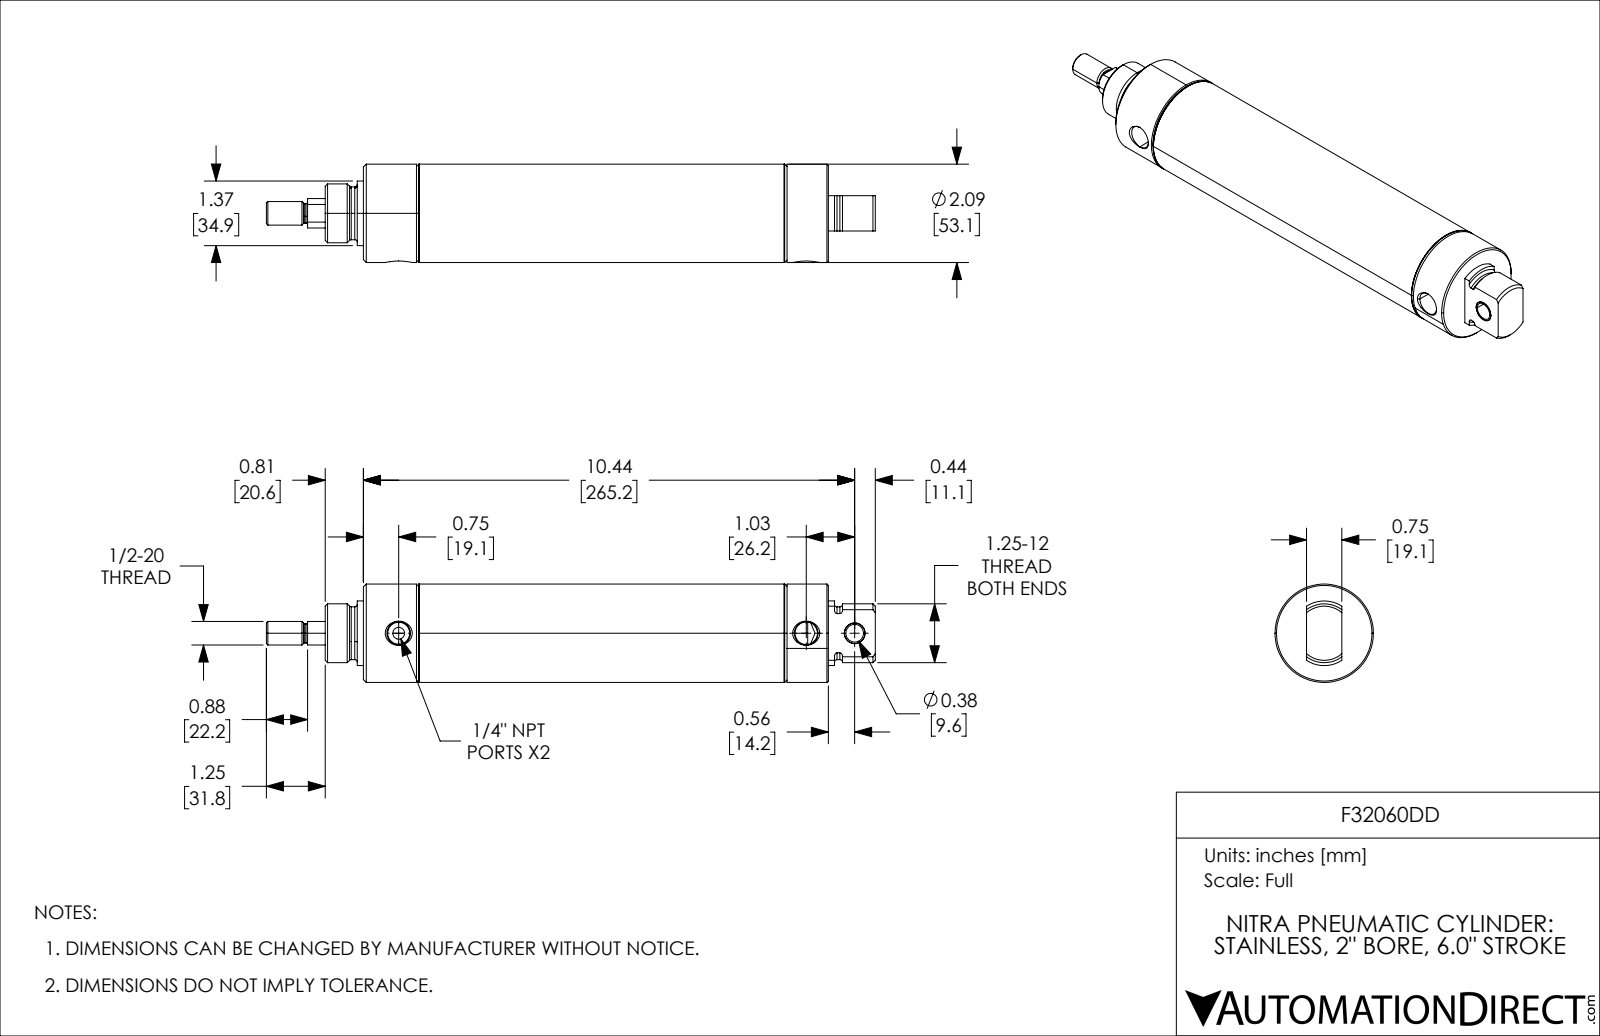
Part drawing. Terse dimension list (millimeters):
name: F32060DD_5; F32060DD_11; F32060DD_7; F32060DD (+2 more)
written by: SolidWorks 2021 (CONFIG_CONTROL_DESIGN)
unit: mm
bodies: 5 solids, 160 faces (31 planar, 60 cylindrical, 69 other)
size: 328.62 × 53.09 × 53.09
volume: 290 012 mm³; area: 119 561 mm²
holes: 1× ⌀6.35, 1× ⌀9.55, 1× ⌀11.15, 1× ⌀12.18, 1× ⌀16.52, 1× ⌀19.05, 1× ⌀49.05
bosses: 1× ⌀53.09, 1× ⌀51.16, 1× ⌀34.87, 1× ⌀31.75, 1× ⌀28.51, 1× ⌀15.88, 1× ⌀12.7, 1× ⌀10.46
rounds: 1× R14.25
face distances: 30.18, 152.4, 182.58, 212.8, 60.4, 30.22, 38.15, 190.55, 220.73, 250.95
hole spacings: 26.17, 219.96, 246.13
